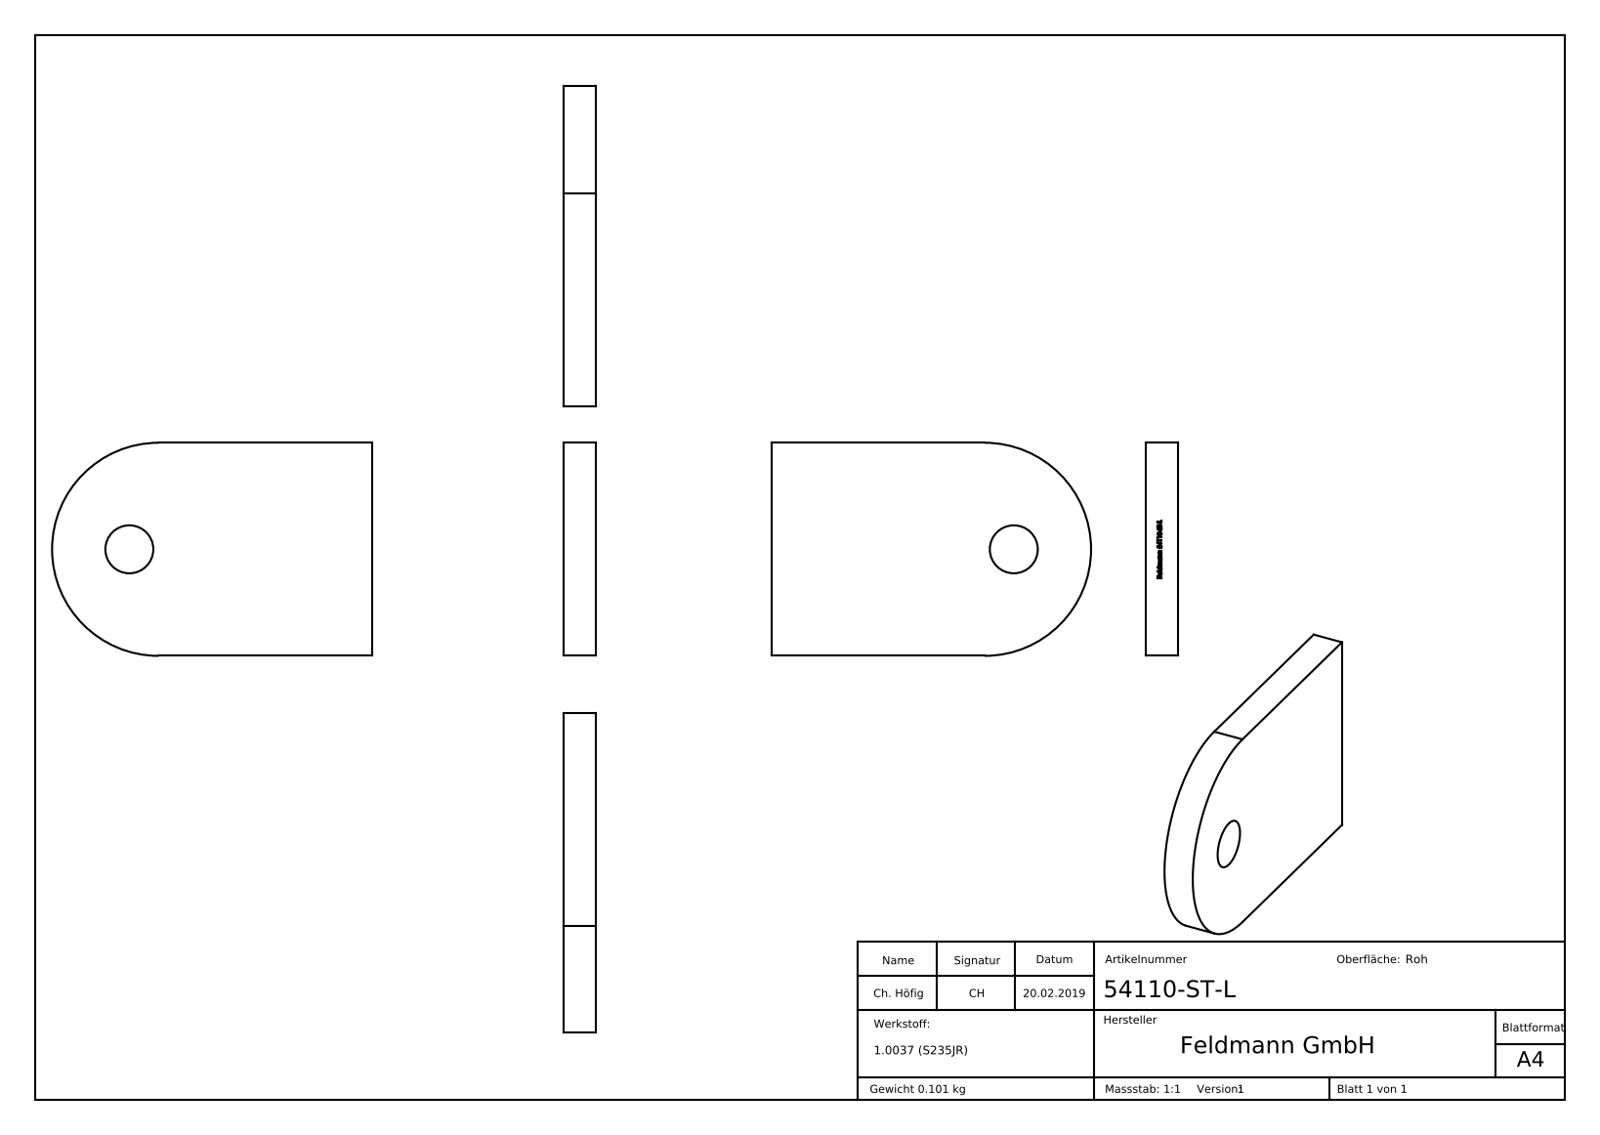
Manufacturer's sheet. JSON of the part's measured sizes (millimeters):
{"part_name": "54110-ST-L", "step_written_by": "SolidWorks 2015 (CONFIG_CONTROL_DESIGN)", "units": "millimeters", "bodies": {"solids": 1, "faces": 221, "planar": 137, "cylindrical": 4, "other": 80}, "overall_size": [60, 40, 6], "volume_mm3": 12988, "surface_area_mm2": 5601, "round_holes": [[9, 1]], "partial_cylinders_radius": [[20, 1]], "face_to_face_distances": [6, 40, 3, 2.66, 0.44, 2.04, 7.73, 5.83, 9.24, 0.53]}
